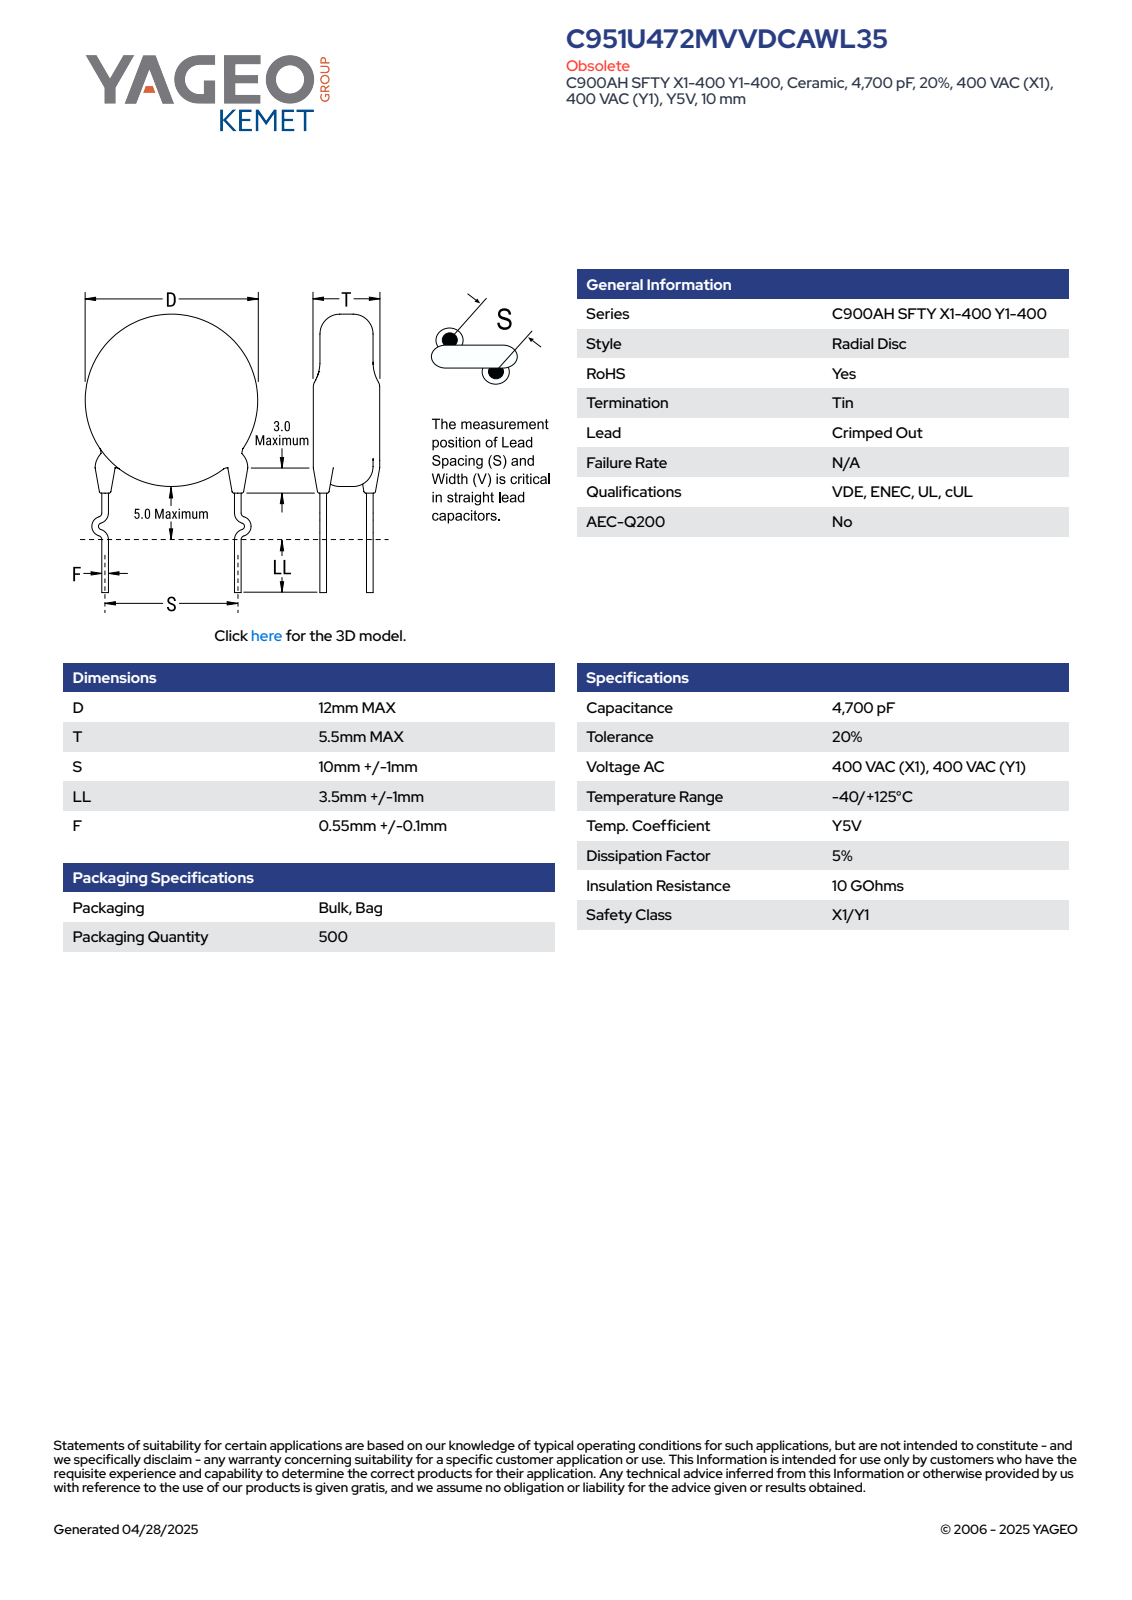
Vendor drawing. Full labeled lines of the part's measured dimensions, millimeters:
Part name (STEP PRODUCT): CCD_KCOC900_D12T5.5S10LL4.5F0.55
STEP written by: SolidWorks 2014 (AUTOMOTIVE_DESIGN)
Units: millimetres
Bodies: 4 solids, 85 faces (63 planar, 6 cylindrical, 16 other)
Overall size (bounding box): 21.5 × 14.84 × 5.5
Volume: 620 mm³ · Surface area: 475 mm²
Round bosses / shafts (diameter × count): ⌀1.2 ×2, ⌀12 ×1
Main face-to-face distances: 5.5, 6.63, 5.39, 1.24, 0.34, 5.1, 0.46, 1, 0.45, 2.58
